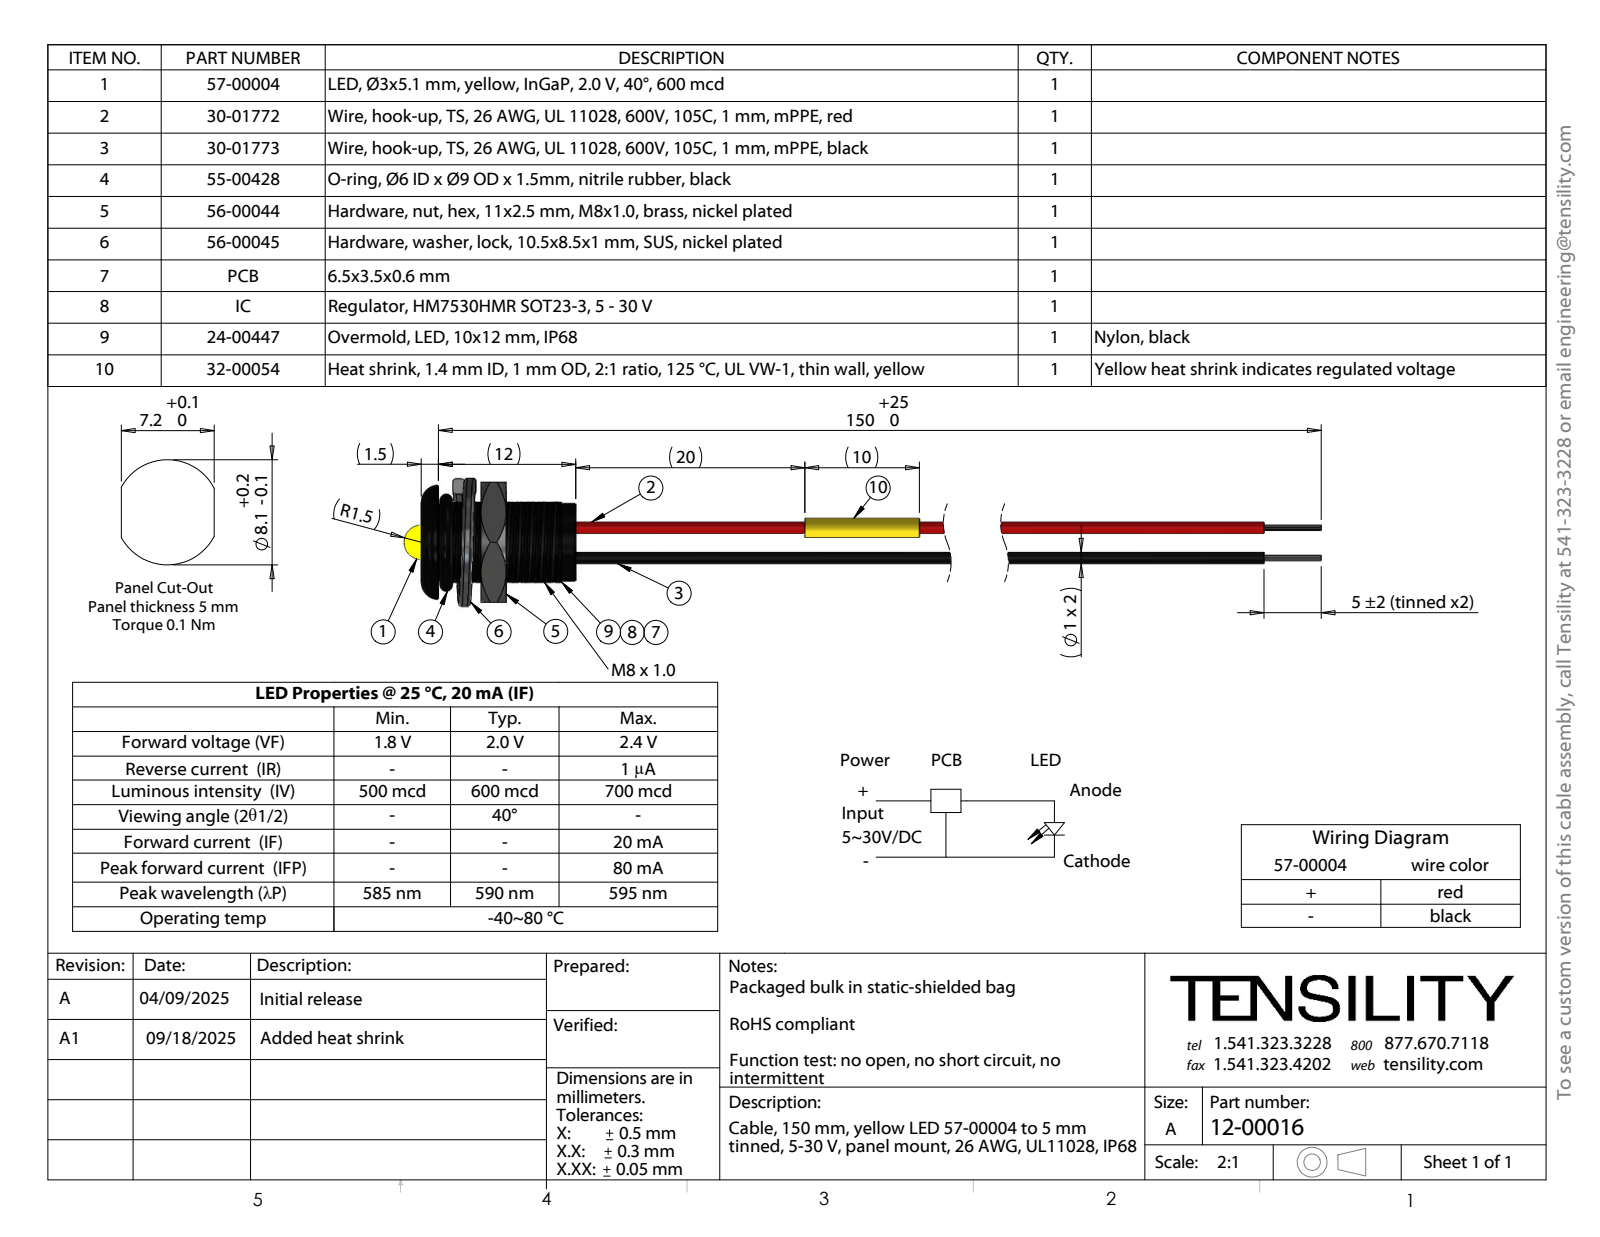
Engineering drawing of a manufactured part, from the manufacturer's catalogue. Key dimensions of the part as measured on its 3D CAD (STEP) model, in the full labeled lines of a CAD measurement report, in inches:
Part name (STEP PRODUCT): 56-00044; 56-00045_Split washer; 12-00016; 24-00447 (+4 more)
STEP written by: SolidWorks 2021 (CONFIG_CONTROL_DESIGN)
Units: inches
Bodies: 57 solids, 555 faces (186 planar, 246 cylindrical, 123 other)
Overall size (bounding box): 6.693 × 0.477 × 0.441
Volume: 0.061 in³ · Surface area: 9.157 in²
Round holes (diameter × count): ⌀0.039 ×2
Round bosses / shafts (diameter × count): ⌀0.039 ×2, ⌀0.02 ×2, ⌀0.268 ×1, ⌀0.118 ×1
Partial cylindrical surfaces — rounded edges, fillets, slot ends (radius × count): R0.137 ×1, R0.157 ×1
Main face-to-face distances: 0.059, 0.531, 0.472, 0.413, 0.205, 0.146, 0.326, 0.292, 0.233, 0.087
Hole centre spacings: 0.014, 0.015, 0.013, 0.098, 0.099, 0.096, 0.096, 0.101
